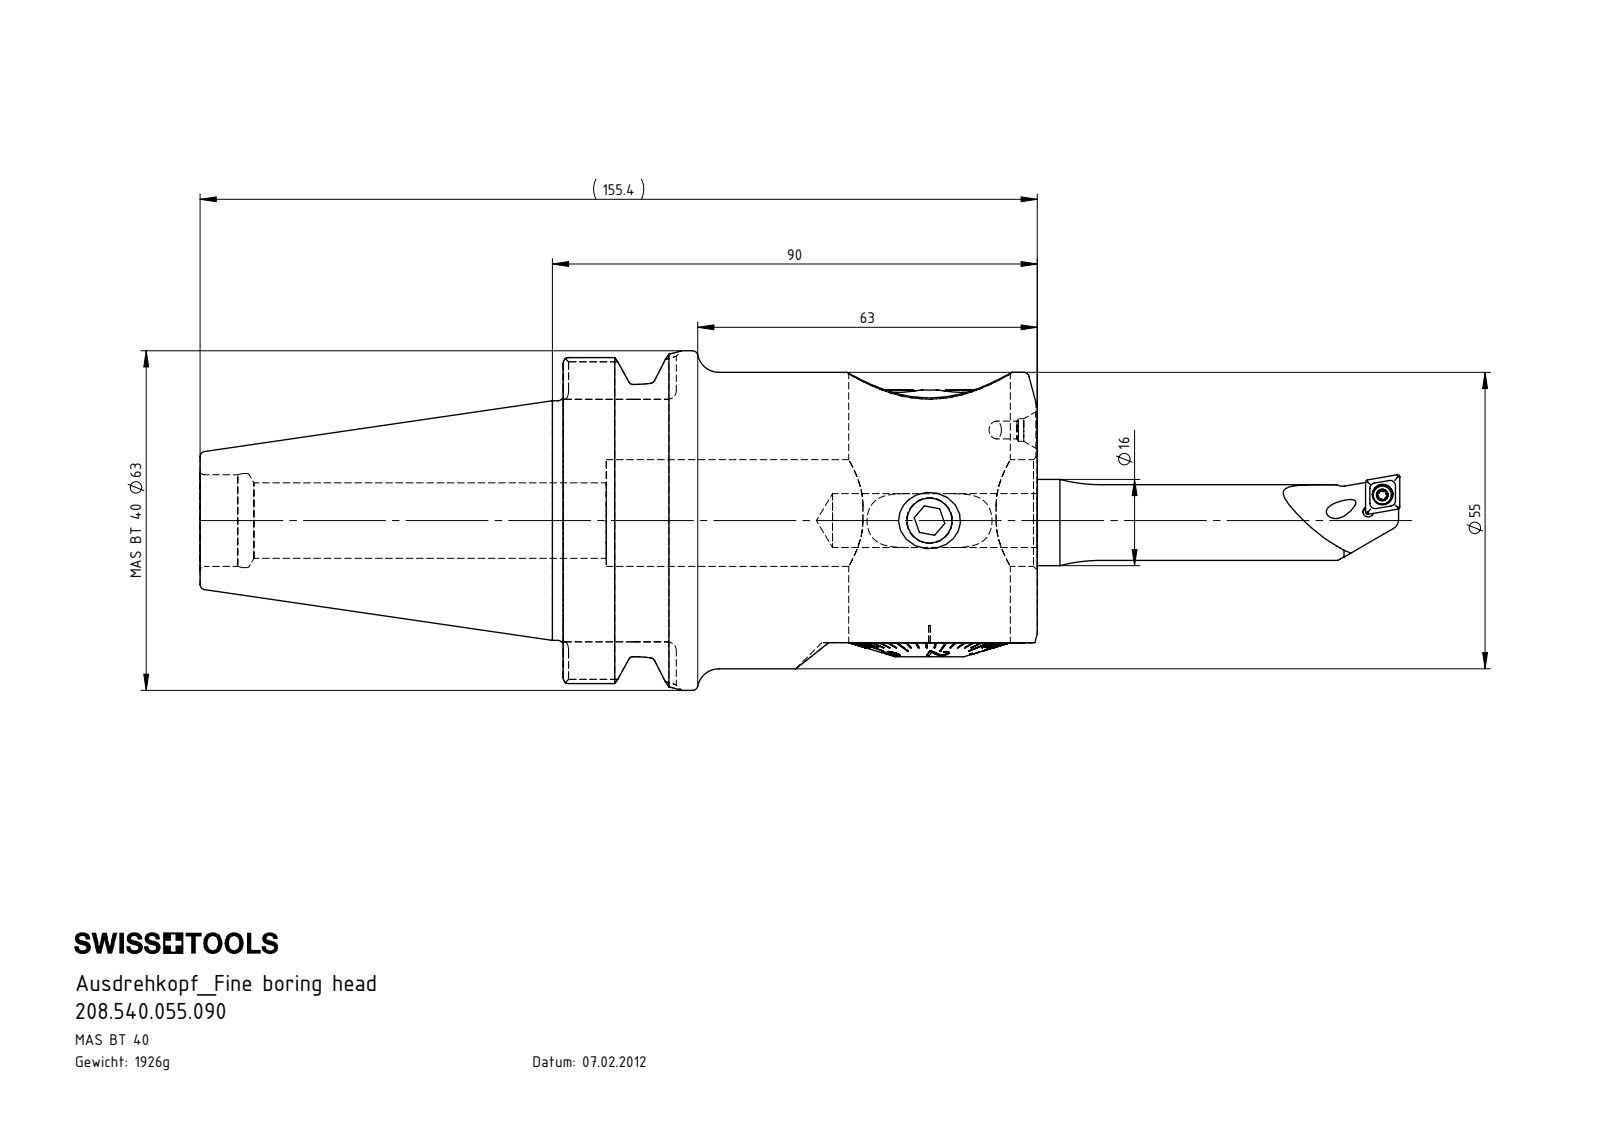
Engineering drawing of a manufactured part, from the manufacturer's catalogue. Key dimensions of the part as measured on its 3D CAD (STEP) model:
Part name (STEP PRODUCT): ISO 4026 - M10 x 16_PreviewCfg; A55-BG2.013.005_C; A55-BG3.011.033_A_gekrzt; WCB-ER2.001.009_A (+8 more)
STEP written by: SolidWorks 2017 (AUTOMOTIVE_DESIGN)
Units: millimetres
Bodies: 14 solids, 615 faces (328 planar, 94 cylindrical, 193 other)
Overall size (bounding box): 155.4 × 63 × 63
Volume: 239 762 mm³ · Surface area: 54 766 mm²
Round holes (diameter × count): ⌀8.5 ×3, ⌀14 ×2, ⌀1.6 ×1, ⌀3.3 ×1, ⌀4.2 ×1, ⌀8 ×1, ⌀10 ×1, ⌀11.4 ×1, ⌀12.4 ×1, ⌀14.2 ×1, ⌀16 ×1, ⌀17 ×1
Round bosses / shafts (diameter × count): ⌀10 ×3, ⌀63 ×1, ⌀55 ×1, ⌀53 ×1, ⌀44.45 ×1, ⌀30 ×1, ⌀29.98 ×1, ⌀29.9 ×1
Partial cylindrical surfaces — rounded edges, fillets, slot ends (radius × count): R1.6 ×8, R0.34 ×6, R0.59 ×6, R1.4 ×4, R1.9 ×4, R3.2 ×3, R2 ×2, R8.5 ×2
Main face-to-face distances: 88, 5.3, 2.8, 2.5, 6.5, 3.7, 1.2, 5.2, 45, 17
Hole centre spacings: 14.5, 7.25, 0.35, 18.83, 19.14, 28.48
